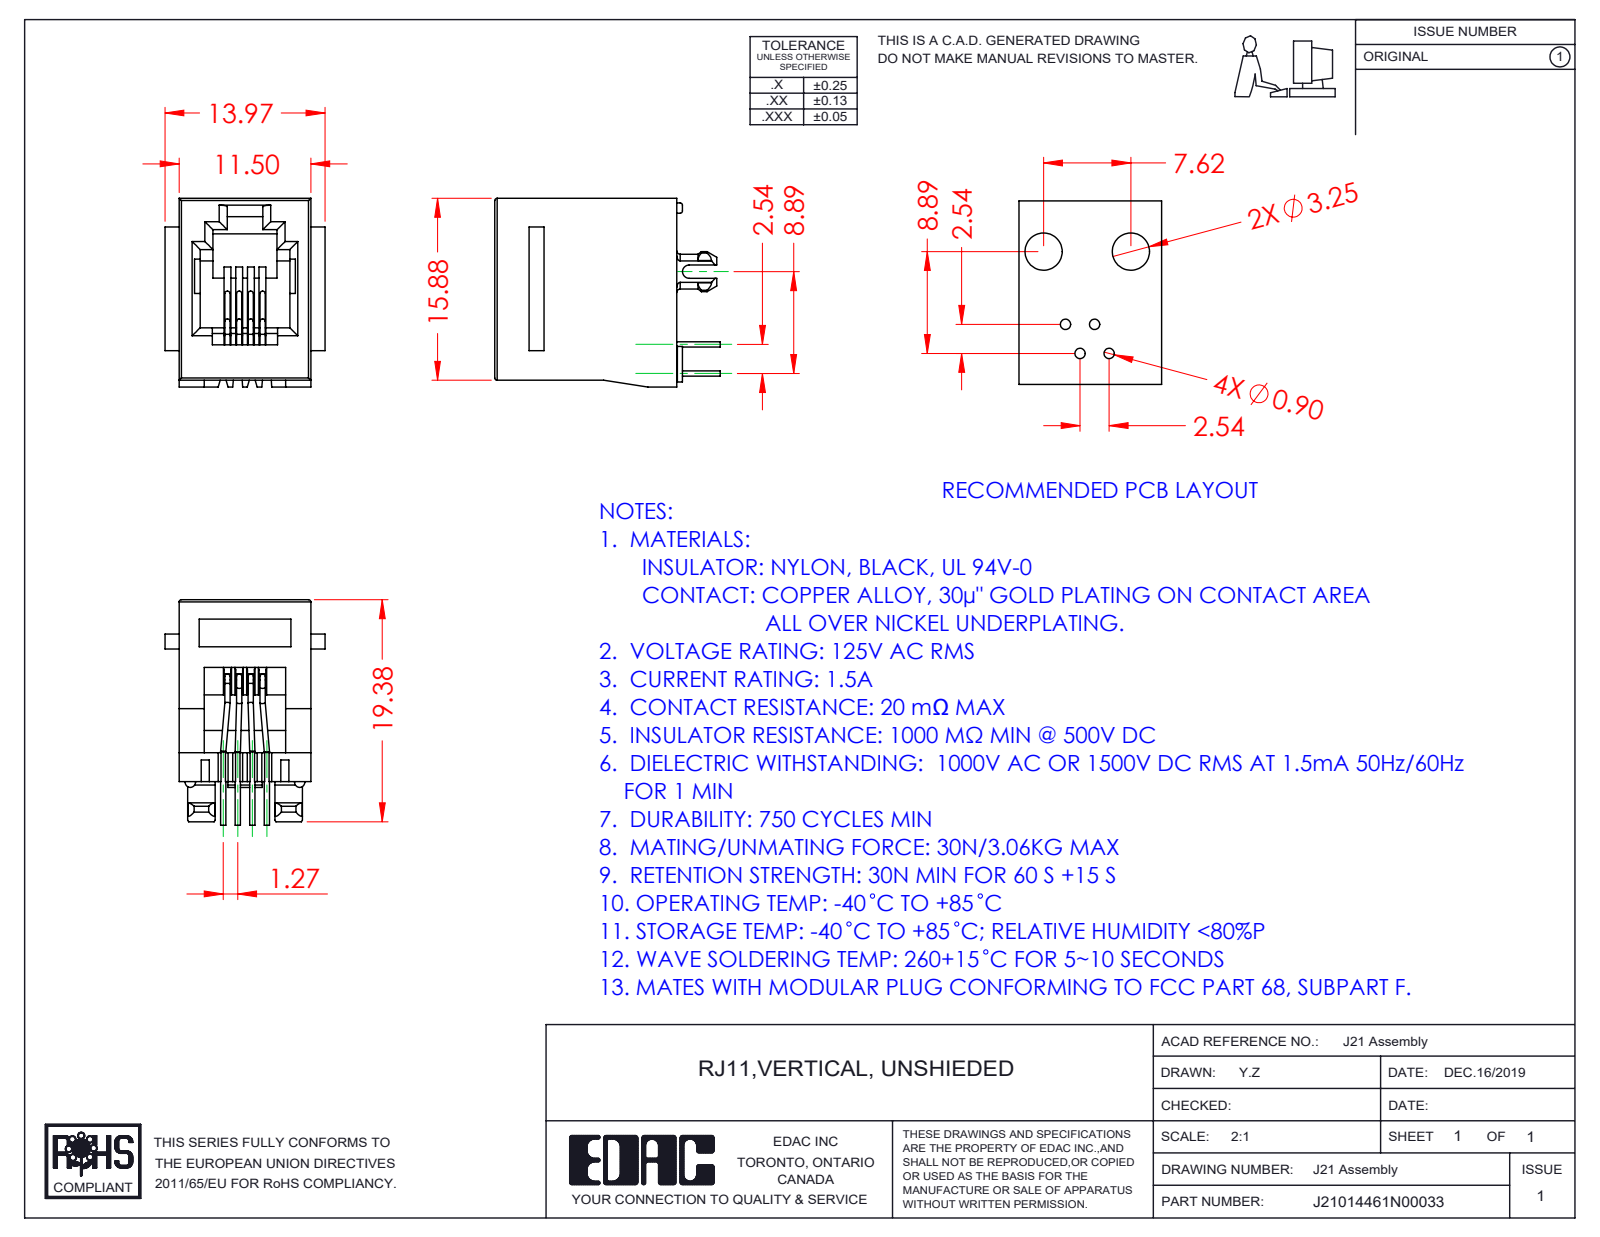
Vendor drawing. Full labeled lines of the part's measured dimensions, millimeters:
Part name (STEP PRODUCT): RJ21014461N00033; 21 Insulator; 21 Contacts
STEP written by: SolidWorks 2016 (CONFIG_CONTROL_DESIGN)
Units: millimetres
Bodies: 5 solids, 369 faces (230 planar, 111 cylindrical, 28 other)
Overall size (bounding box): 19.68 × 16.48 × 13.97
Volume: 1 616 mm³ · Surface area: 2 564 mm²
Round holes (diameter × count): ⌀2 ×2
Round bosses / shafts (diameter × count): ⌀0.46 ×24
Partial cylindrical surfaces — rounded edges, fillets, slot ends (radius × count): R0.5 ×9, R0.7 ×9, R0.2 ×7, R0.23 ×4, R0.45 ×2, R1.52 ×2, R1.75 ×2, R0.57 ×1
Main face-to-face distances: 11.5, 1.6, 15.88, 1.02, 7.2, 0.6, 2.95, 8.55, 2.04, 1.35
Hole centre spacings: 8.4
